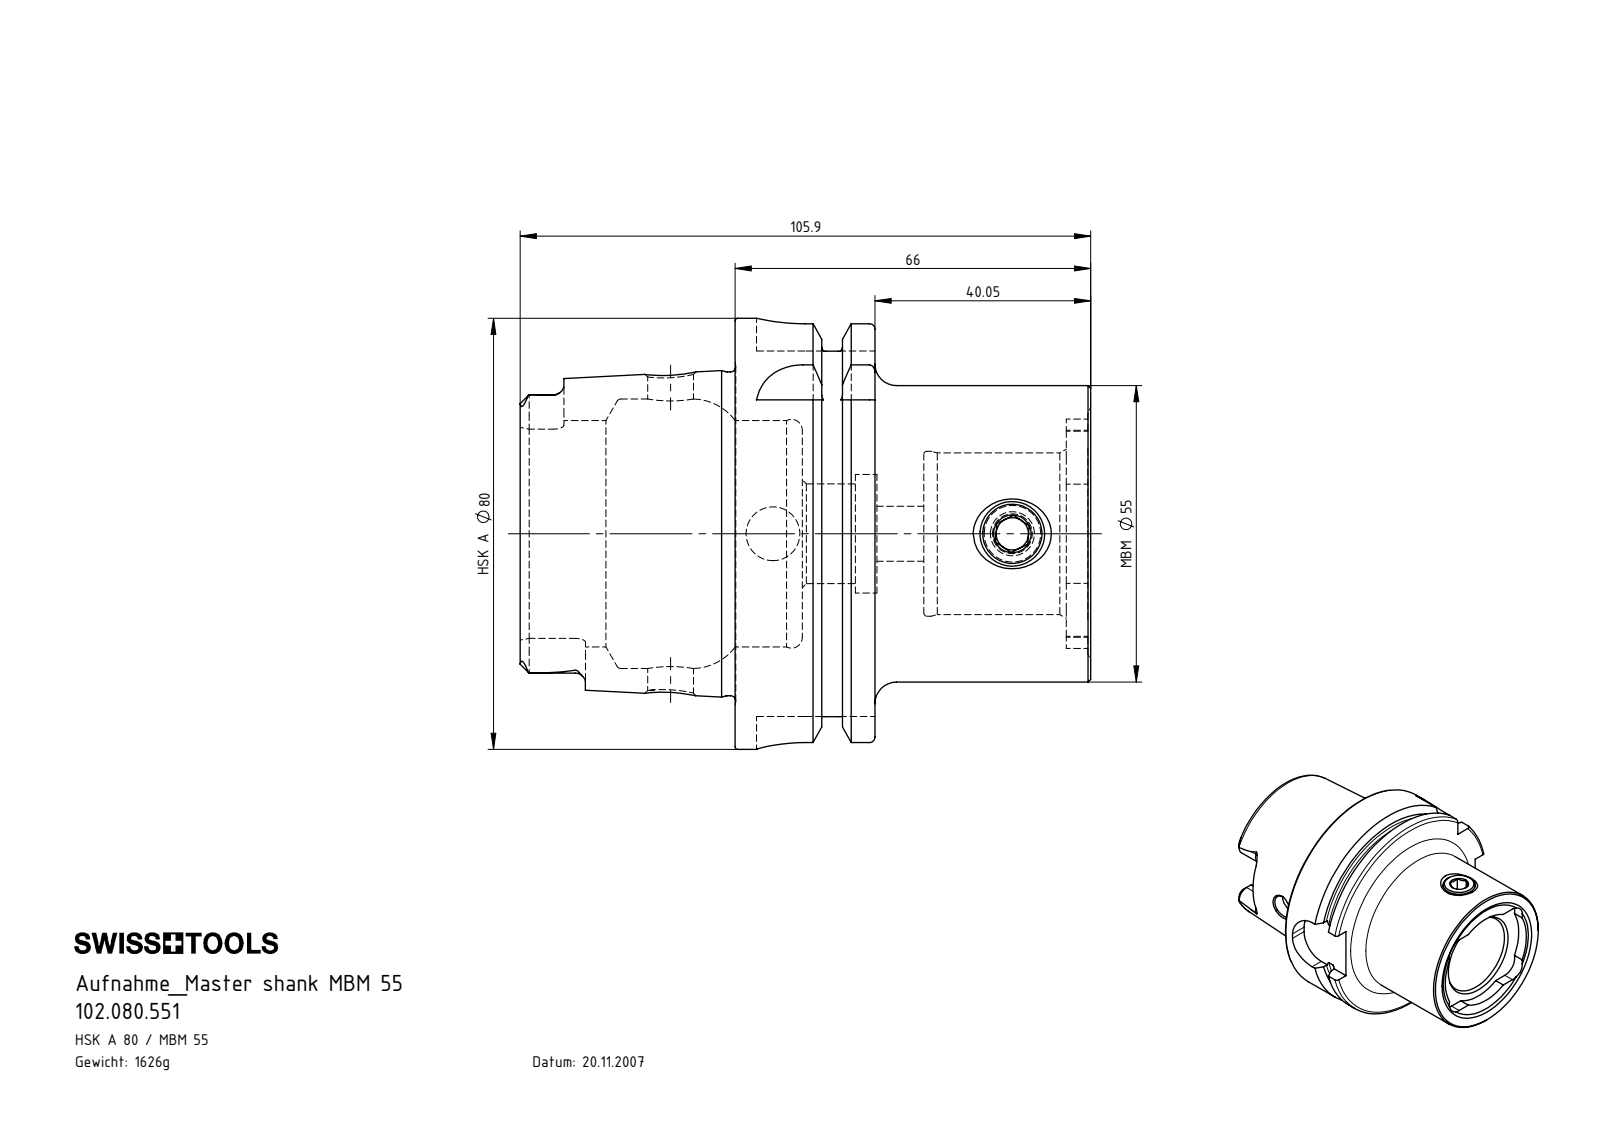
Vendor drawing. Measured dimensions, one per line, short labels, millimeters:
name: HA8-MB5.K01.066_B_Fertigbearbeitung; 102.080.551; MB5-ER1.001.017_A
written by: SolidWorks 2017 (CONFIG_CONTROL_DESIGN)
unit: mm
bodies: 2 solids, 221 faces (70 planar, 66 cylindrical, 85 other)
size: 105.9 × 80 × 80
volume: 207 179 mm³; area: 44 186 mm²
holes: 1× ⌀6, 1× ⌀8.5, 1× ⌀10, 1× ⌀10.2, 1× ⌀11, 1× ⌀18.5, 1× ⌀22, 1× ⌀30, 1× ⌀30.6, 1× ⌀42, 1× ⌀50
bosses: 1× ⌀80, 1× ⌀69.95, 1× ⌀60.06, 1× ⌀55, 1× ⌀12
rounds: 6× R1.9, 4× R3.88, 4× R5.2, 4× R9, 1× R18.5, 1× R21.27
face distances: 25.95, 12.45, 13.5, 9.05, 35, 22.55, 66, 53.55, 40.05, 31
hole spacings: 44.45
